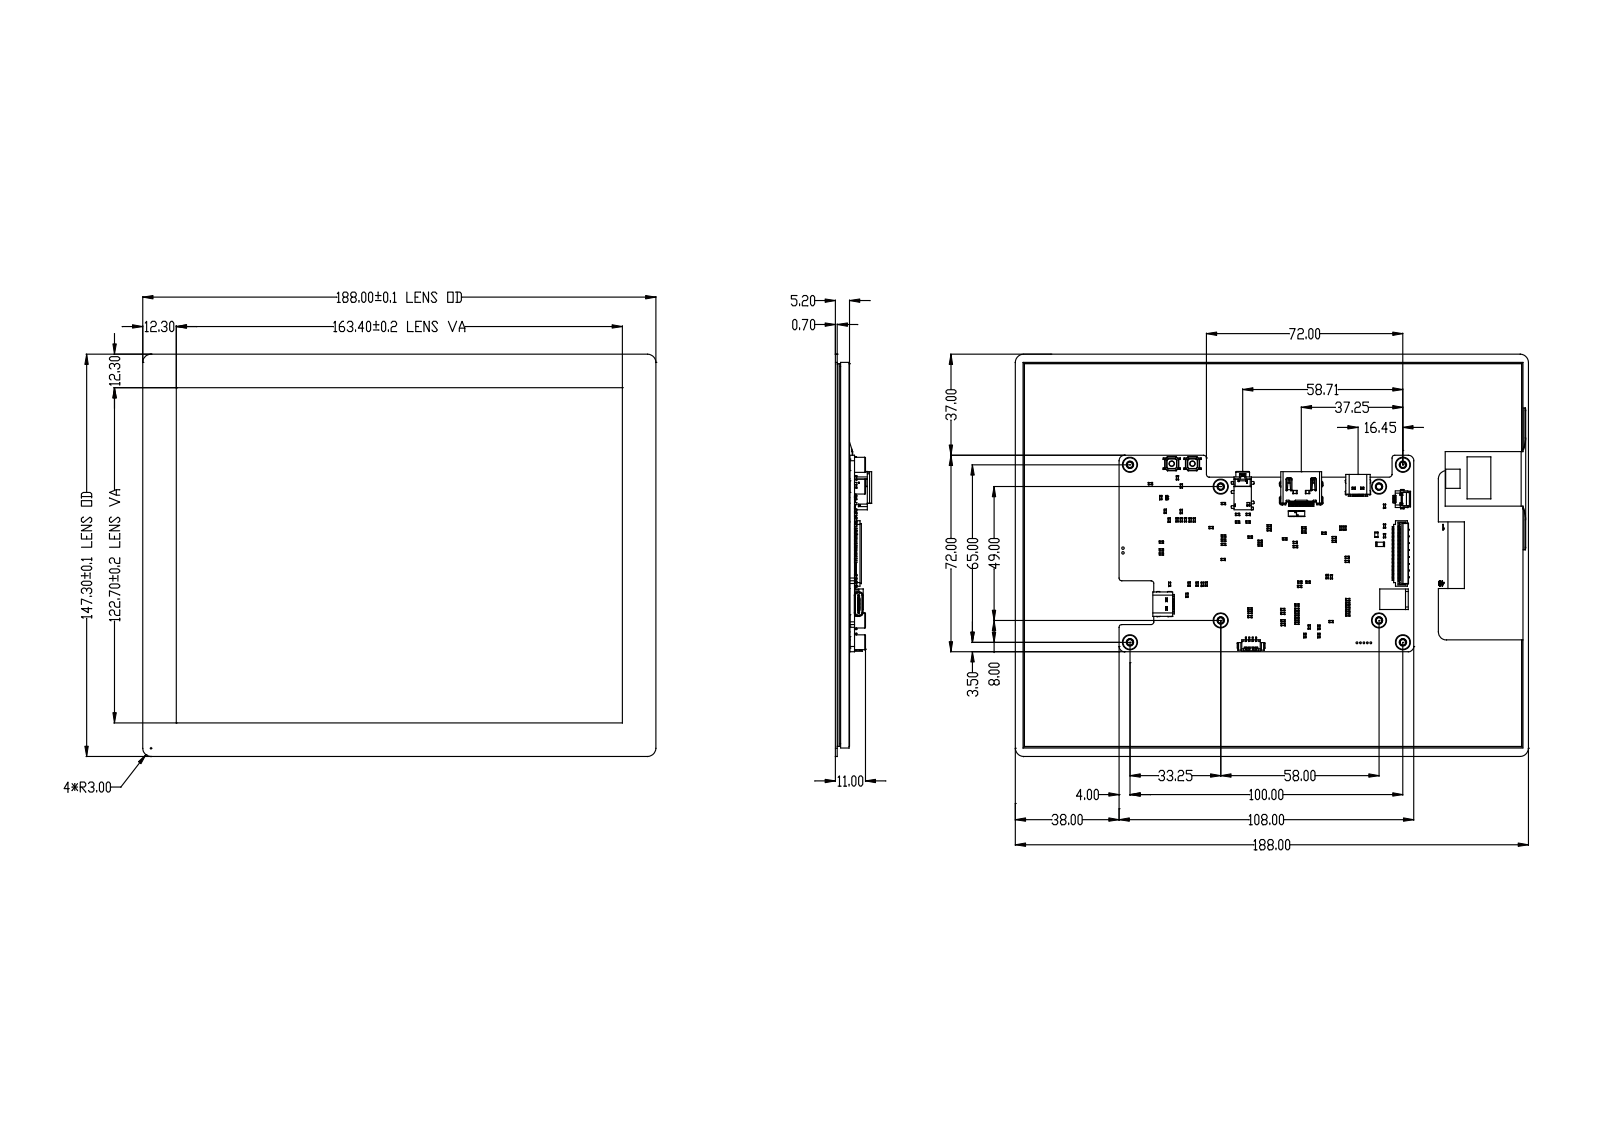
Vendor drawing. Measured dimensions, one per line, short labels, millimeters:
name: HS080XOB-IM4080; 8INCH-TOUCH-20230918; 8INCH-LCD_TOUCH-20230918_ASM; HL2236_KICAD_PCB (+8 more)
written by: CREO PARAMETRIC BY PTC INC, 2021063 (CONFIG_CONTROL_DESIGN)
unit: mm
bodies: 159 solids, 7154 faces (4890 planar, 2073 cylindrical, 191 other)
size: 188 × 147.3 × 13.32
volume: 126 555 mm³; area: 137 132 mm²
holes: 8× ⌀2.5, 8× ⌀4.3, 5× ⌀0.65, 4× ⌀0.6, 2× ⌀0.4, 2× ⌀0.9, 2× ⌀1.4, 1× ⌀3.6
bosses: 8× ⌀5.5, 8× ⌀4.19, 4× ⌀0.5, 2× ⌀2, 2× ⌀1.3, 1× ⌀5
rounds: 80× R0.1, 76× R0.2, 47× R0.3, 42× R0.15, 40× R0.25, 25× R0.12, 18× R0.5, 15× R0.4
face distances: 4.3, 1.1, 1.95, 0.85, 5.15, 3.2, 1, 3.3, 1.85, 5.2
hole spacings: 1.27, 2.54, 3.81, 5.78, 11.86, 34.2, 49, 55.42
